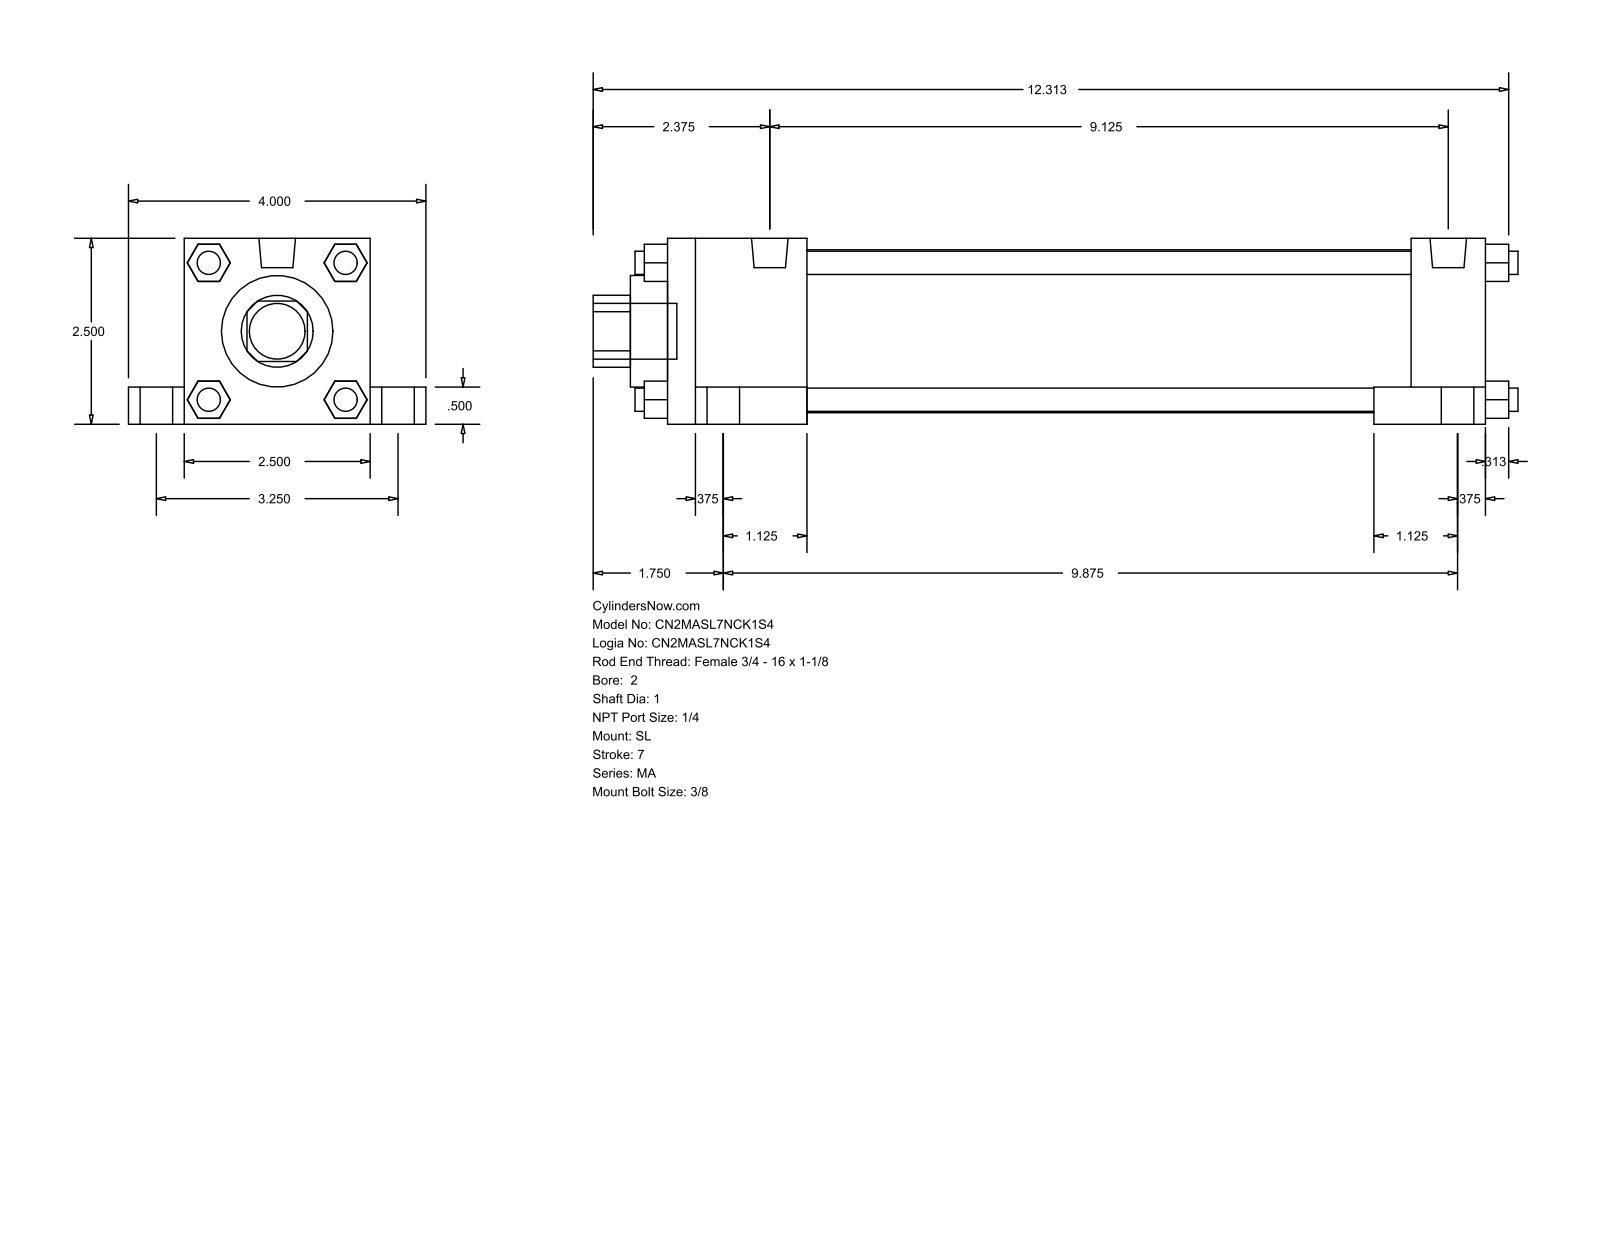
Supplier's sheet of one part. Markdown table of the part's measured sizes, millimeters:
| quantity | value |
| --- | --- |
| part name | MA_SL__0200_1 |
| STEP written by | GSSL Pune (CONFIG_CONTROL_DESIGN) |
| units | millimeters |
| bodies | 0 solids, 148 faces (112 planar, 36 cylindrical, 0 other) |
| overall size | 315.91 × 101.6 × 63.5 |
| round holes (diameter × count) | 25.4 × 1, 38.1 × 1, 55.63 × 1 |
| round bosses / shafts (diameter × count) | 7.94 × 8, 17.46 × 4, 11.11 × 4, 12.49 × 2, 19.05 × 1 |
| partial cylindrical surfaces (radius × count) | 12.29 × 1 |
| main face-to-face distances | 63.5, 12.7, 279.4, 19.05, 82.55, 25.4, 50.8, 47.63, 231.77, 254 |
